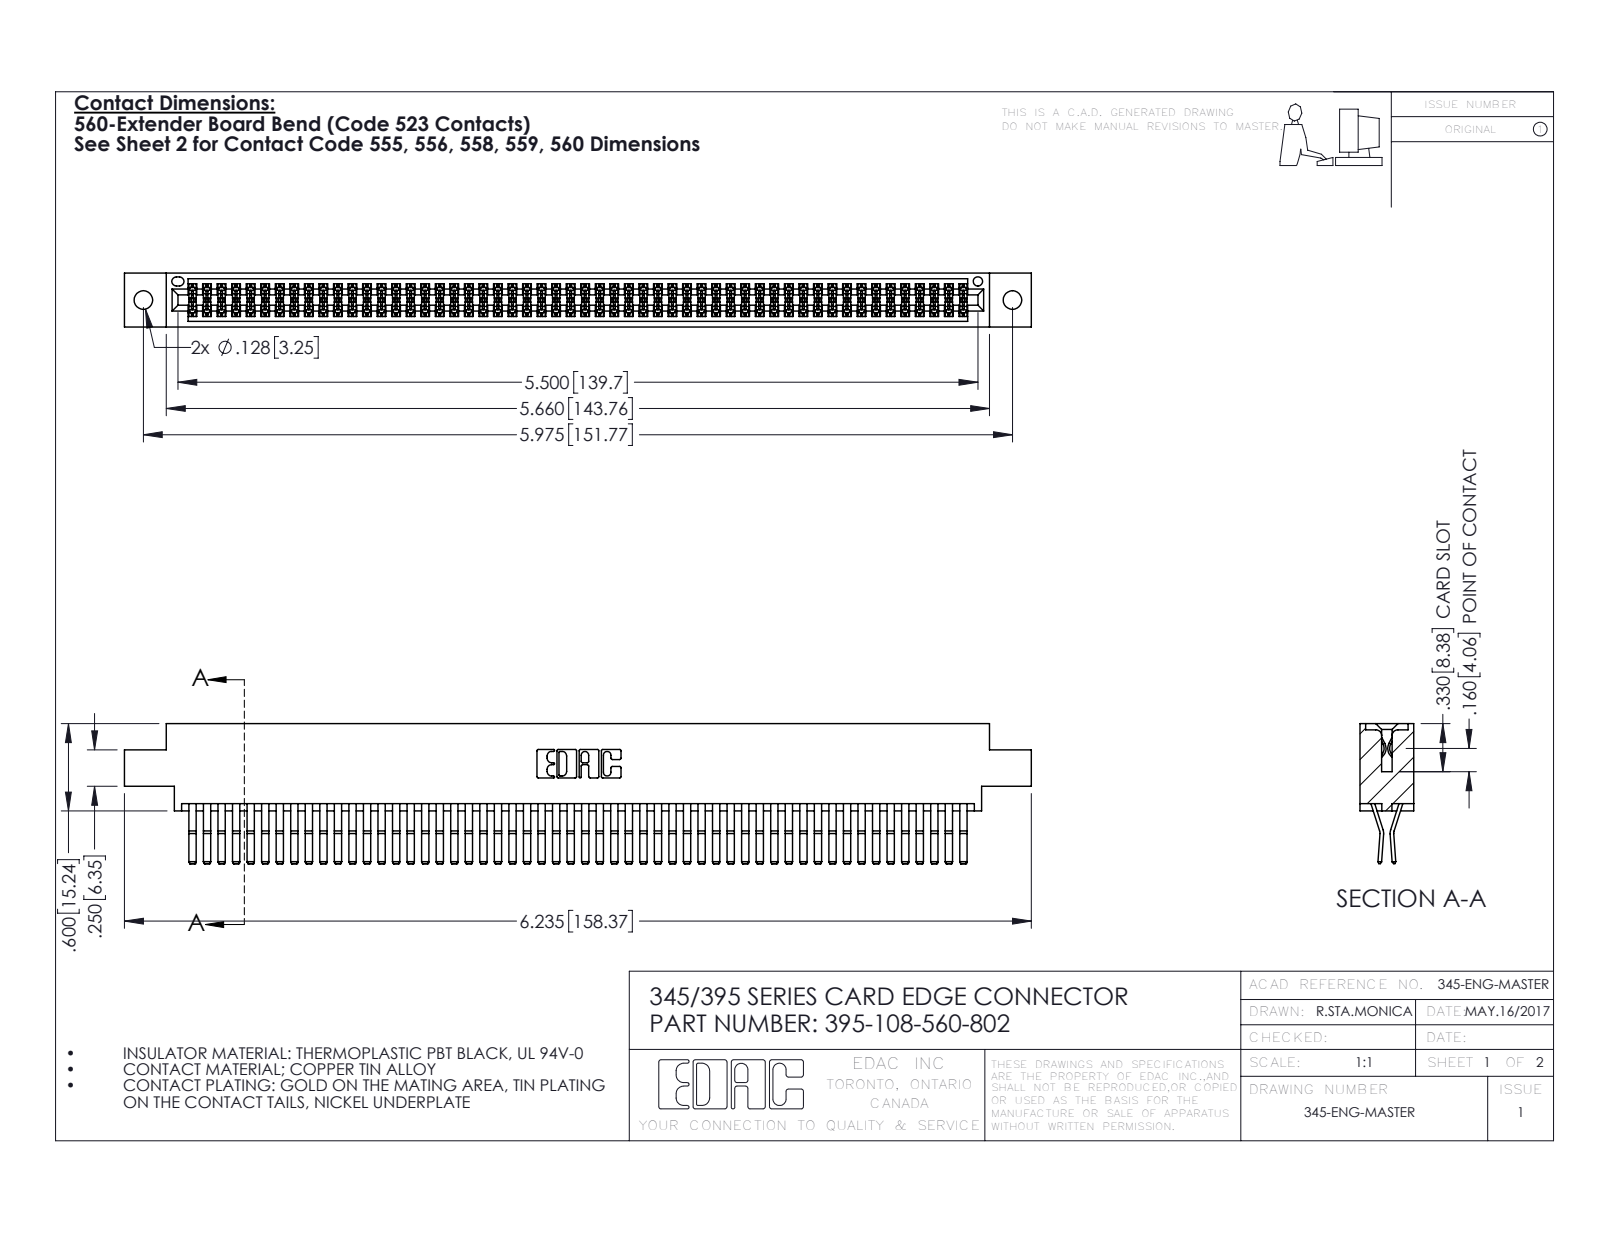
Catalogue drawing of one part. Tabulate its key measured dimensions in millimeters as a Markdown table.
| quantity | value |
| --- | --- |
| part name | 345 Part_0.170 Offset - 0.128 Dia; 345-292-001_560 Tail; 395-108-560-802 |
| STEP written by | SolidWorks 2016 (CONFIG_CONTROL_DESIGN) |
| units | millimeters |
| bodies | 109 solids, 5746 faces (3648 planar, 2098 cylindrical, 0 other) |
| overall size | 158.4 × 24.4 × 9.4 |
| volume | 16 100 mm³ |
| surface area | 25 650 mm² |
| round holes (diameter × count) | 3.3 × 2, 1.6 × 1 |
| partial cylindrical surfaces (radius × count) | 0.2 × 162, 0.3 × 22, 0.2 × 6, 0.8 × 6, 0.7 × 3, 0.3 × 2, 0.4 × 2, 0.5 × 2 |
| main face-to-face distances | 0.6, 7.6, 1.8, 9.4, 5.1, 2.5, 6.9, 5.7, 4.4, 3.8 |
| hole center spacings | 6.9, 145.8, 151.8 |
